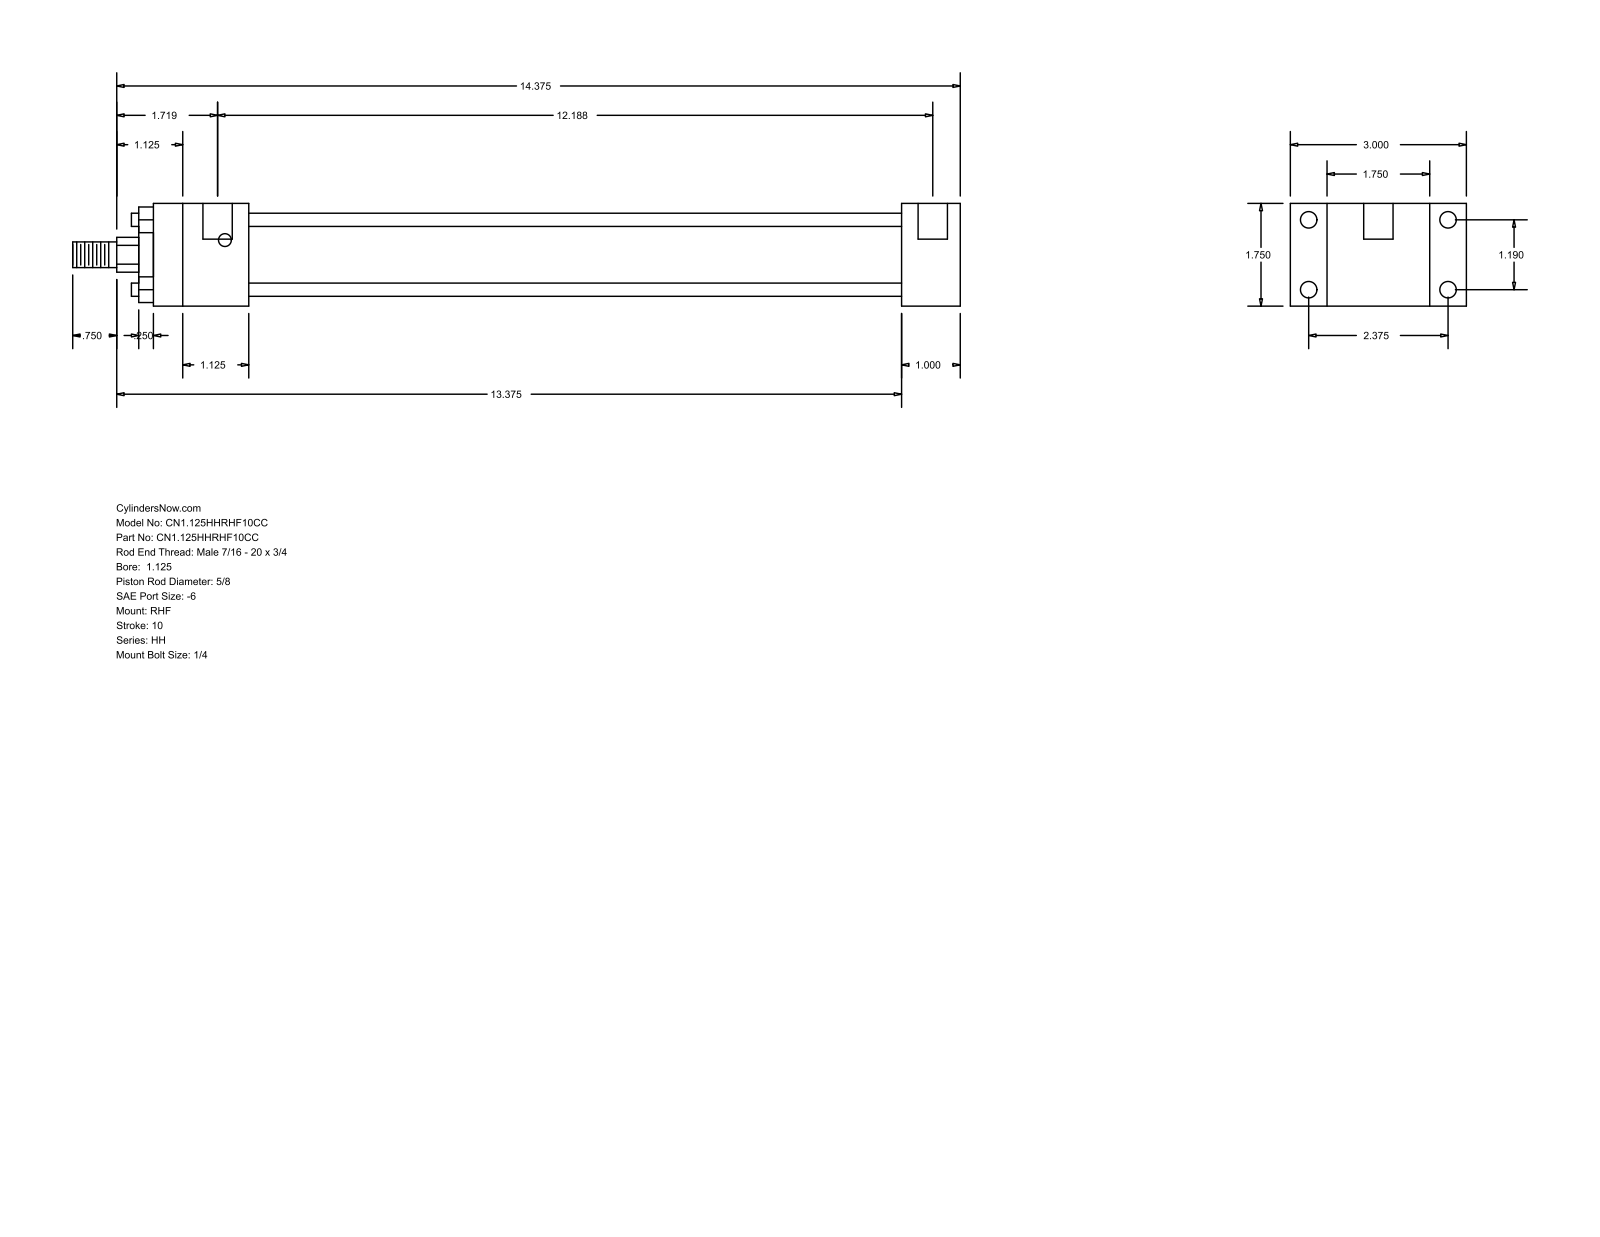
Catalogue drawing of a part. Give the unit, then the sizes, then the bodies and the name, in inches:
Units: inches
Overall size (bounding box): 15.125 × 3 × 1.75
Round holes (diameter × count): ⌀0.219 ×4, ⌀0.281 ×4, ⌀0.5 ×2
Round bosses / shafts (diameter × count): ⌀0.225 ×4, ⌀1.375 ×1, ⌀1.125 ×1, ⌀0.625 ×1, ⌀0.437 ×1
Partial cylindrical surfaces — rounded edges, fillets, slot ends (radius × count): R0.297 ×1
Main face-to-face distances: 1.75, 0.625, 2.375, 1, 3, 11.125, 12.125, 1.625, 12.75, 13.75
Hole centre spacings: 1.19, 2.375, 2.656, 12.063, 0.125, 12.187
Bodies: 0 solids, 88 faces (60 planar, 28 cylindrical, 0 other)
Part name (STEP PRODUCT): HH_RHF__0112_0.625
STEP written by: GSSL Pune (CONFIG_CONTROL_DESIGN)
